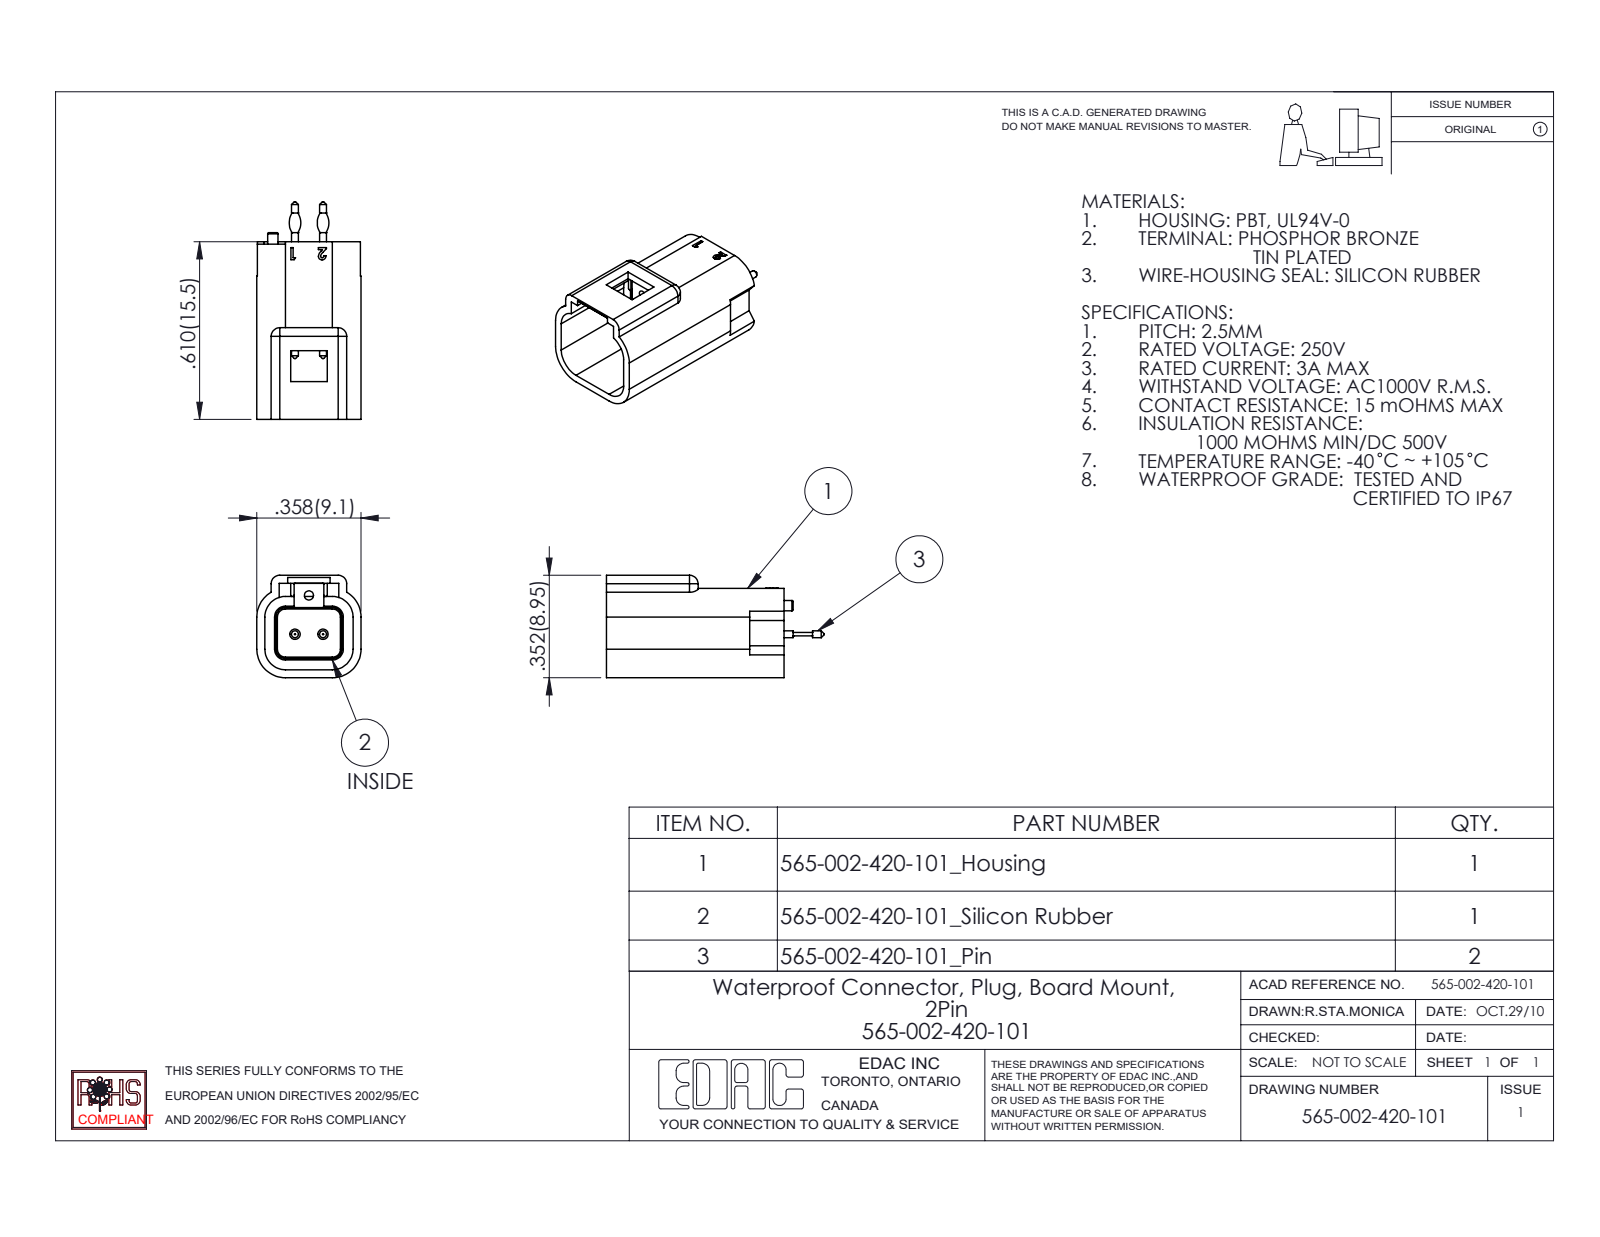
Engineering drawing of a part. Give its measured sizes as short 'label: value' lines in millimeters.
name: 565-002-420-101_Silicon Rubber; 565-002-420-101_Housing; 565-002-420-101_Pin; 565-002-420-101
written by: SolidWorks 2020 (AUTOMOTIVE_DESIGN)
unit: mm
bodies: 4 solids, 404 faces (198 planar, 140 cylindrical, 66 other)
size: 19 × 9.1 × 8.95
volume: 511 mm³; area: 1 485 mm²
holes: 1× ⌀0.8
bosses: 2× ⌀0.6, 1× ⌀0.9
rounds: 16× R0.14, 8× R0.1, 8× R0.24, 5× R0.75, 4× R0.7, 4× R0.95, 4× R1.55, 4× R1.61
face distances: 0.7, 1.15, 0.85, 7.7, 5.3, 8.4, 2, 7.1, 8.25, 0.55
